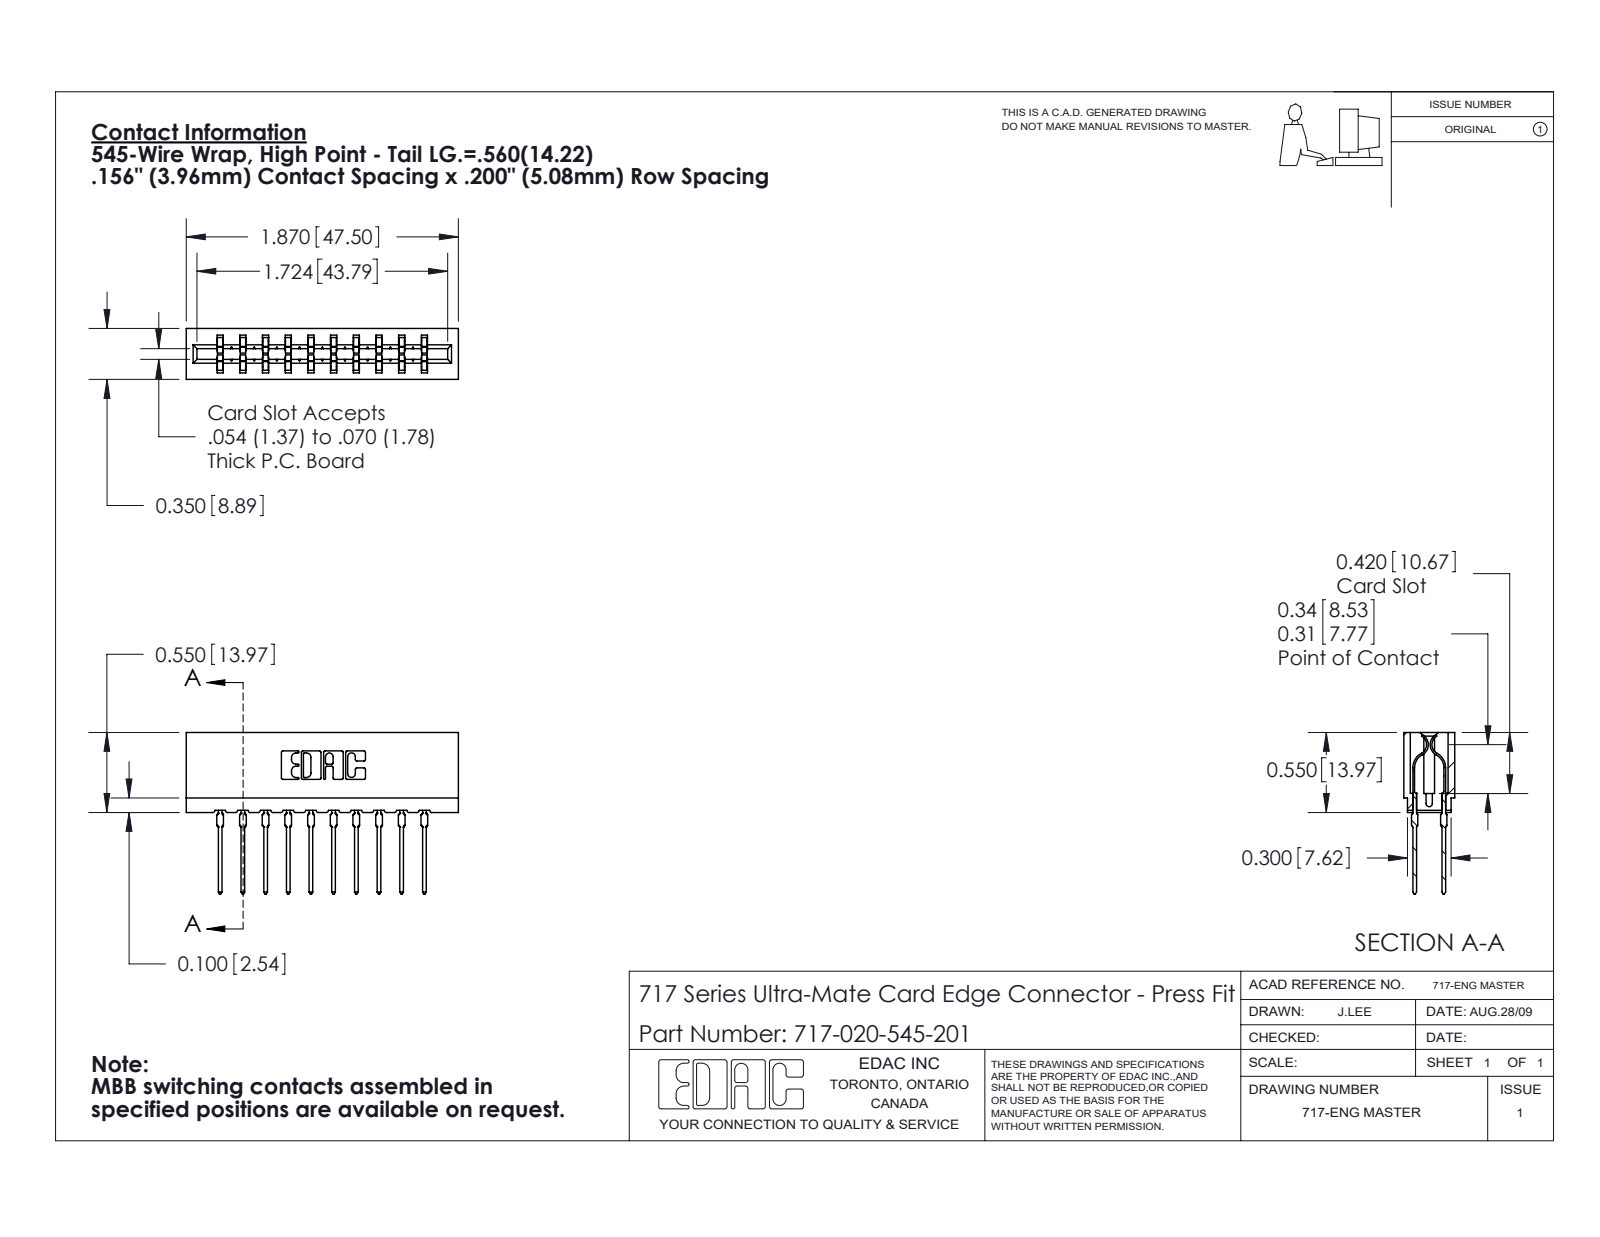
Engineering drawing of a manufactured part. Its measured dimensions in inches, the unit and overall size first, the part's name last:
Units: inches
Overall size (bounding box): 1.87 × 1.109 × 0.35
Partial cylindrical surfaces — rounded edges, fillets, slot ends (radius × count): R0.021 ×40, R0.01 ×22, R0.015 ×20, R0.005 ×8, R0.011 ×8, R0.007 ×6, R0.031 ×6, R0.026 ×3
Main face-to-face distances: 0.156, 0.212, 0.138, 0.624, 0.35, 0.198, 0.468, 0.312, 0.063, 0.287
Volume: 0.264 in³ · Surface area: 10.1 in²
Bodies: 21 solids, 1894 faces (984 planar, 390 cylindrical, 520 other)
Part name (STEP PRODUCT): 745-292-001_545; 717-020-545-201; 717 Part_Insulator Option - 06
STEP written by: SolidWorks 2020 (CONFIG_CONTROL_DESIGN)
